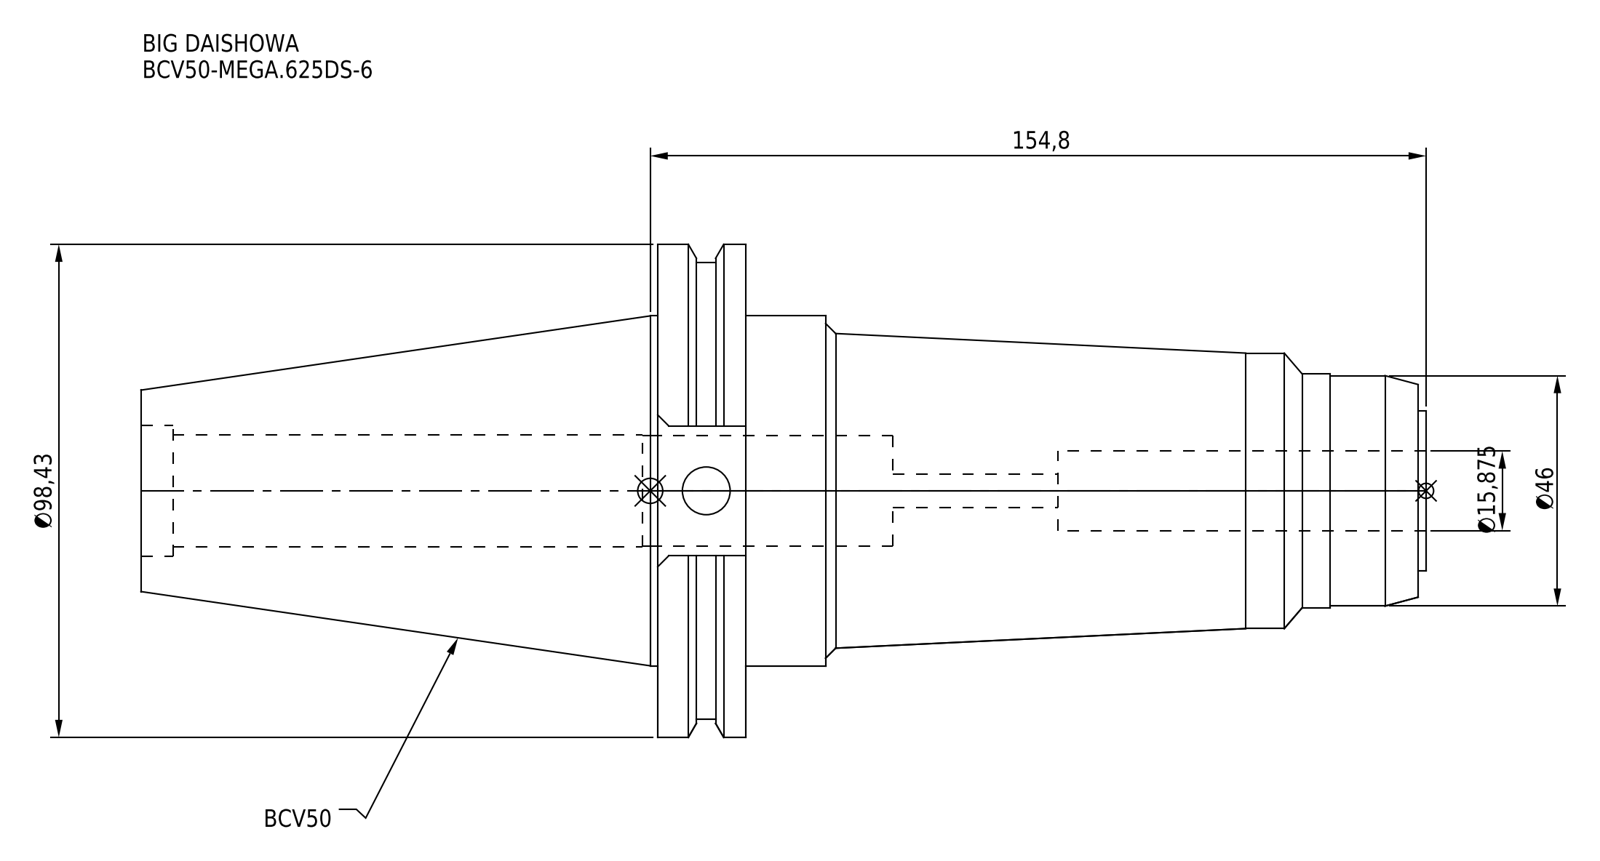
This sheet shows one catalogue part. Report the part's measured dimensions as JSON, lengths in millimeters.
{"part_name": "BCV50-MEGA_625DS-6", "step_written_by": "CREO PARAMETRIC BY PTC INC, 2016380 (AUTOMOTIVE_DESIGN)", "units": "millimeters", "bodies": {"solids": 1, "faces": 72, "planar": 26, "cylindrical": 32, "other": 14}, "overall_size": [256.4, 98.42, 94.95], "volume_mm3": 652076, "surface_area_mm2": 74337, "round_holes": [[6.8, 1], [9.53, 1], [15.88, 1], [22, 1], [22.3, 1], [26.23, 1]], "round_bosses_or_shafts": [[98.42, 1], [91.29, 1], [69.85, 1], [55, 1], [46.7, 1], [46, 1], [31.9, 1]], "face_to_face_distances": [17.55, 120.65, 103.1, 134.15, 151.7, 254.8, 1.6, 135.75, 153.3, 256.4]}
